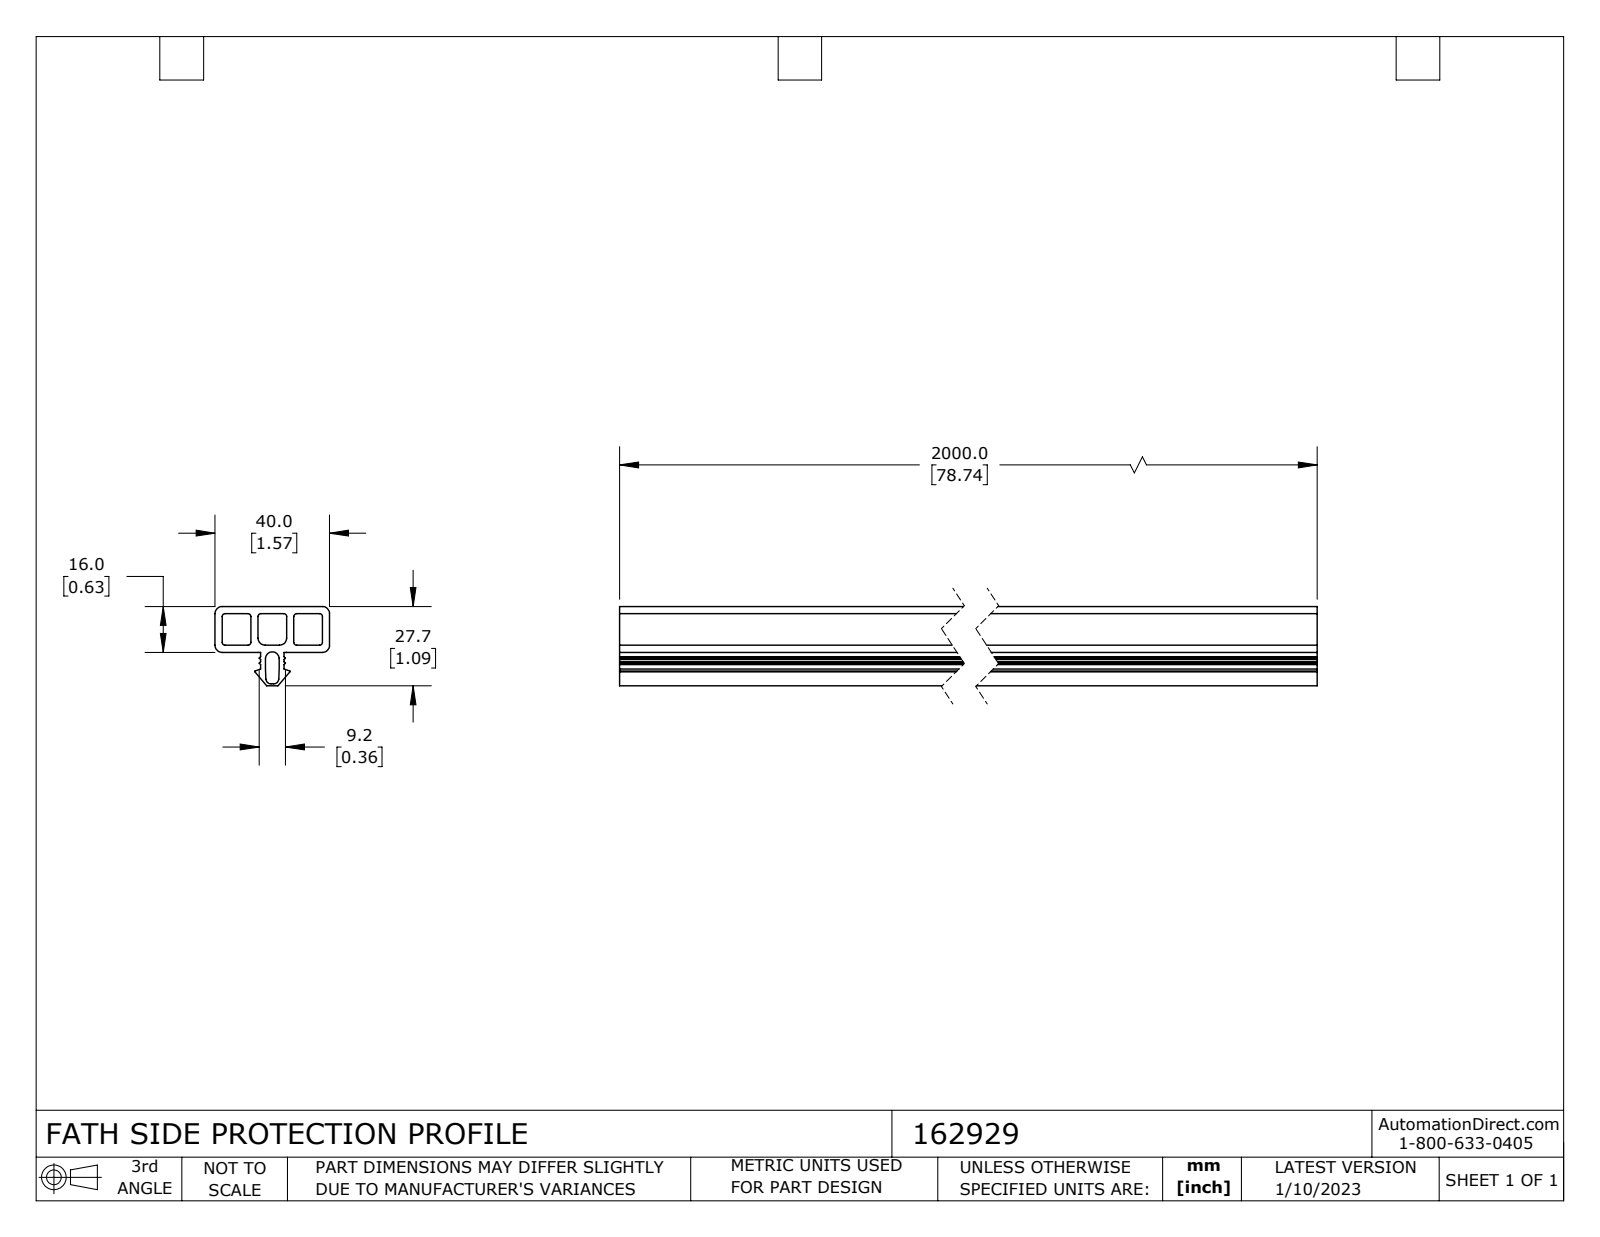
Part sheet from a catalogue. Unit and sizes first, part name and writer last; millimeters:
Units: millimetres
Overall size (bounding box): 2000 × 40 × 27.7
Partial cylindrical surfaces — rounded edges, fillets, slot ends (radius × count): R1 ×12, R2.5 ×6, R1.8 ×2, R2.4 ×1
Main face-to-face distances: 2.5, 13.5, 12.5, 16, 10, 11, 25, 22.5, 40, 2.5
Volume: 719 600 mm³ · Surface area: 564 700 mm²
Bodies: 1 solid, 66 faces (43 planar, 21 cylindrical, 2 other)
Part name (STEP PRODUCT): 162929
STEP written by: SolidWorks 2021 (CONFIG_CONTROL_DESIGN)
